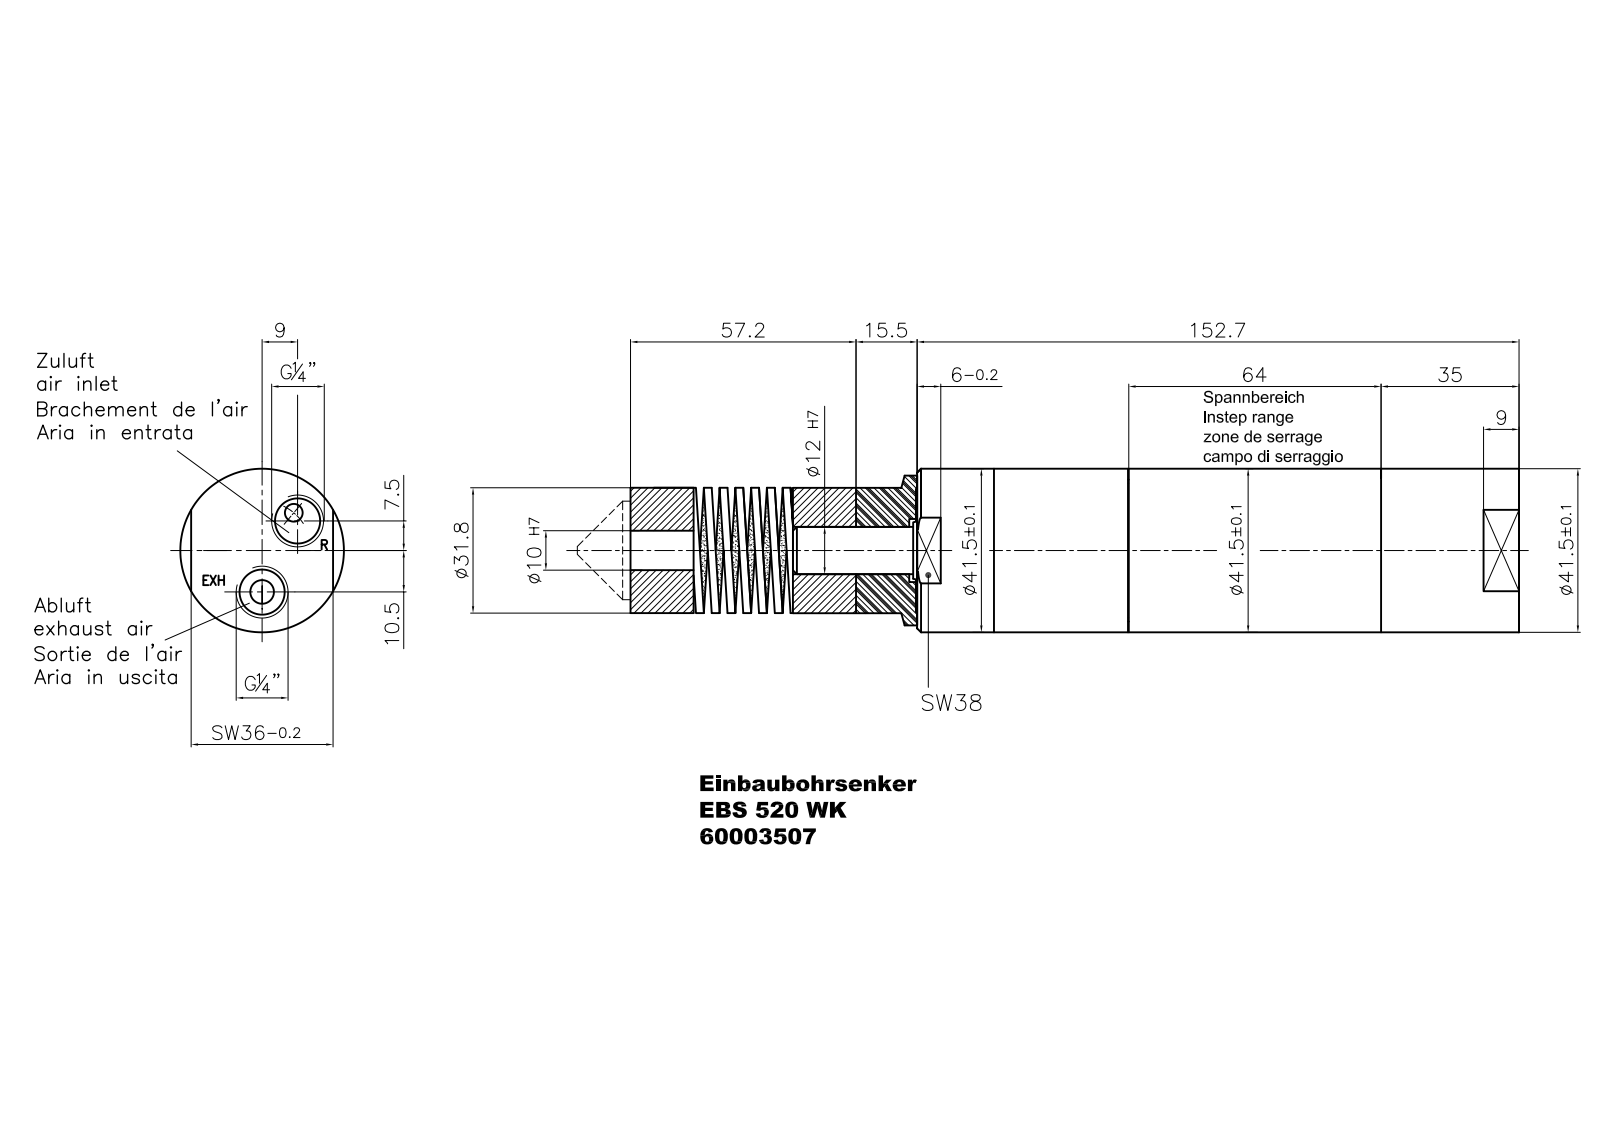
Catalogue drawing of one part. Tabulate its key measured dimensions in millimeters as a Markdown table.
| quantity | value |
| --- | --- |
| part name | EBS 520 WK_60003507 |
| STEP written by | Autodesk Inventor 2012 (AUTOMOTIVE_DESIGN) |
| units | millimeters |
| bodies | 2 solids, 242 faces (145 planar, 64 cylindrical, 33 other) |
| overall size | 225.4 × 41.5 × 41.5 |
| volume | 249 775 mm³ |
| surface area | 42 458 mm² |
| round holes (diameter × count) | 4 × 2, 8 × 2, 11.45 × 2, 1.6 × 1, 6 × 1, 10 × 1, 12 × 1 |
| round bosses / shafts (diameter × count) | 7 × 2, 41.5 × 1, 38 × 1, 36 × 1, 32 × 1, 31.8 × 1 |
| partial cylindrical surfaces (radius × count) | 5 × 2, 2 × 1, 2.25 × 1, 7.5 × 1, 8.28 × 1, 17.5 × 1 |
| main face-to-face distances | 24.2, 1, 225.4, 41.2, 184.2, 16, 17, 40.2, 25.2, 209.4 |
| hole center spacings | 10.5, 11.72, 20.12, 41.2 |
